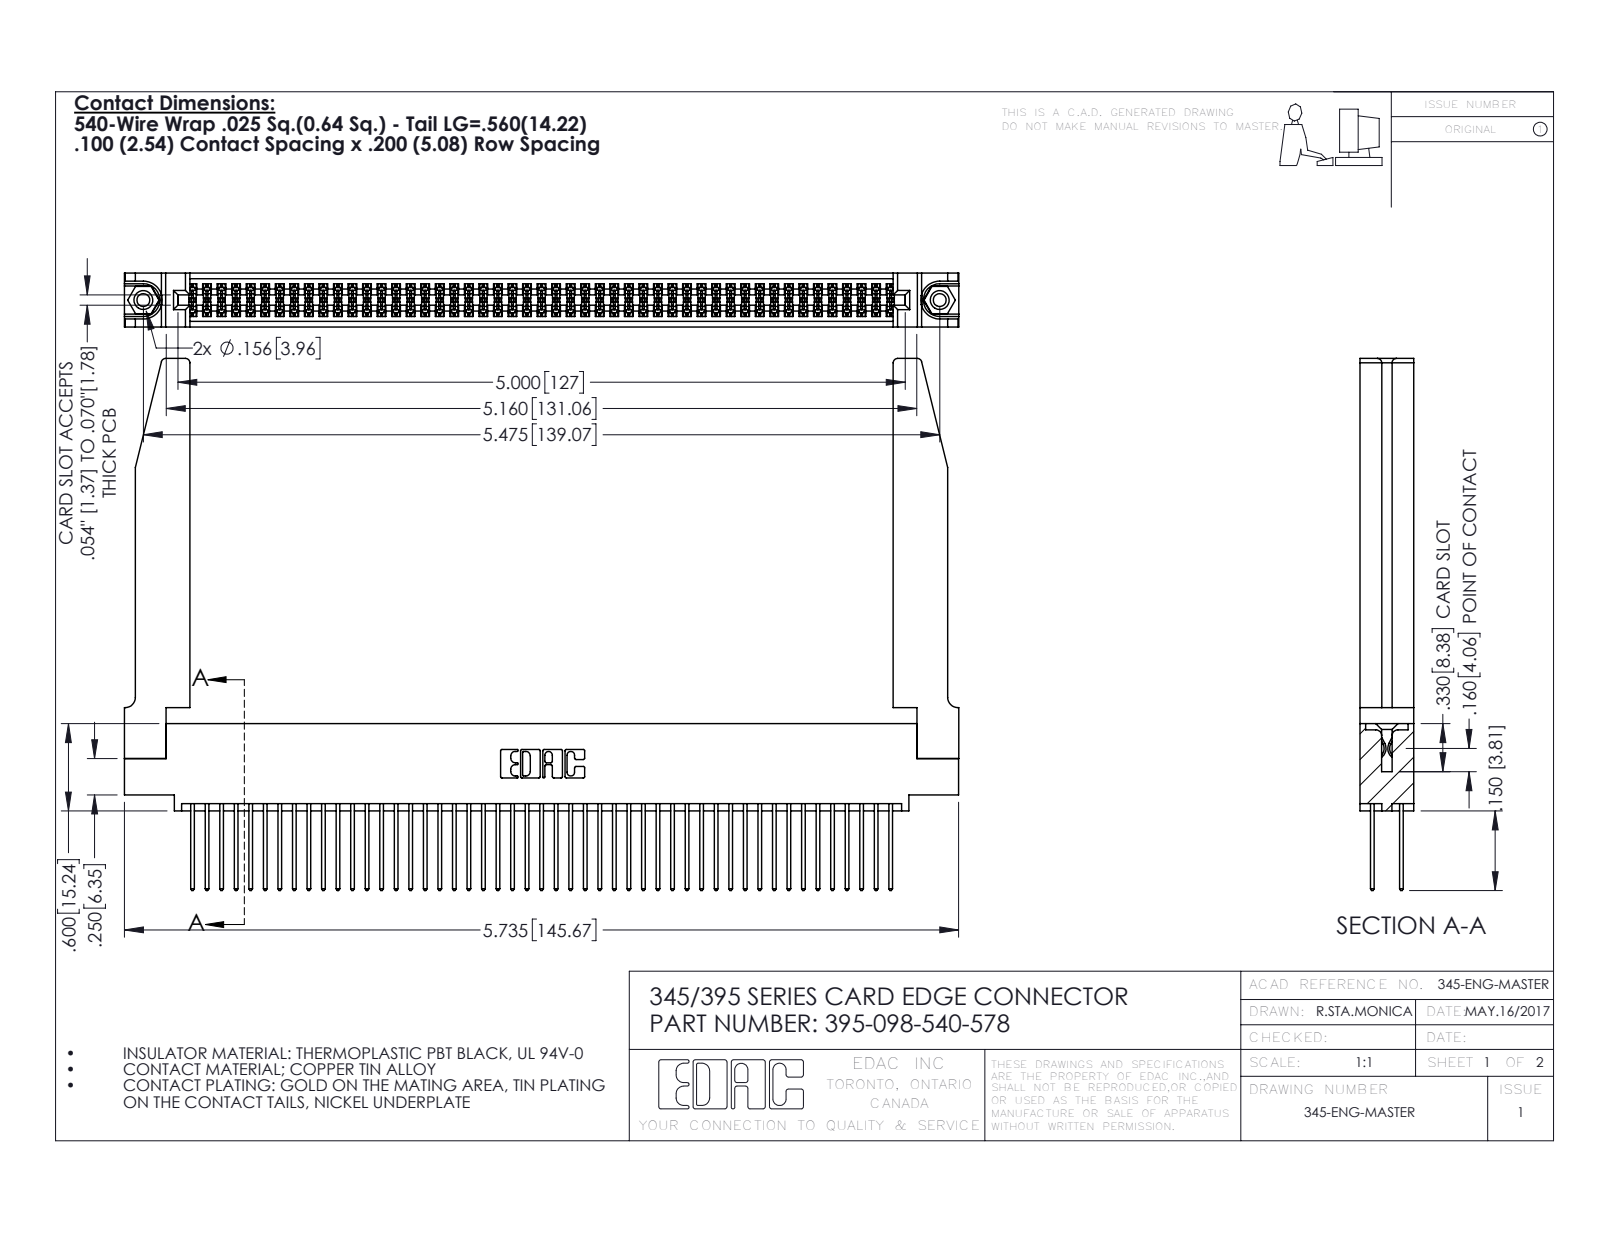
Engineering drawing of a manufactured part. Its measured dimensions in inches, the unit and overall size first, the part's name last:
Units: inches
Overall size (bounding box): 5.736 × 3.657 × 0.37
Round holes (diameter × count): ⌀0.089 ×2, ⌀0.125 ×2, ⌀0.156 ×2, ⌀0.064 ×1
Round bosses / shafts (diameter × count): ⌀0.155 ×2
Partial cylindrical surfaces — rounded edges, fillets, slot ends (radius × count): R0.006 ×147, R0.01 ×98, R0.01 ×22, R0.03 ×8, R0.007 ×6, R0.031 ×6, R0.026 ×3, R0.014 ×2
Main face-to-face distances: 0.072, 0.298, 0.37, 0.098, 0.272, 0.025, 0.2, 0.225, 0.175, 0.148
Hole centre spacings: 0.27, 5.239, 5.475
Volume: 1.36 in³ · Surface area: 46.88 in²
Bodies: 103 solids, 5264 faces (3460 planar, 1752 cylindrical, 52 other)
Part name (STEP PRODUCT): 345-250-001_345-250-001-102; 395-098-540-578; 345 Part_0.110 Offset - 0.156 Dia-TH; 345-292-001_345-293-140 (+1 more)
STEP written by: SolidWorks 2016 (CONFIG_CONTROL_DESIGN)
